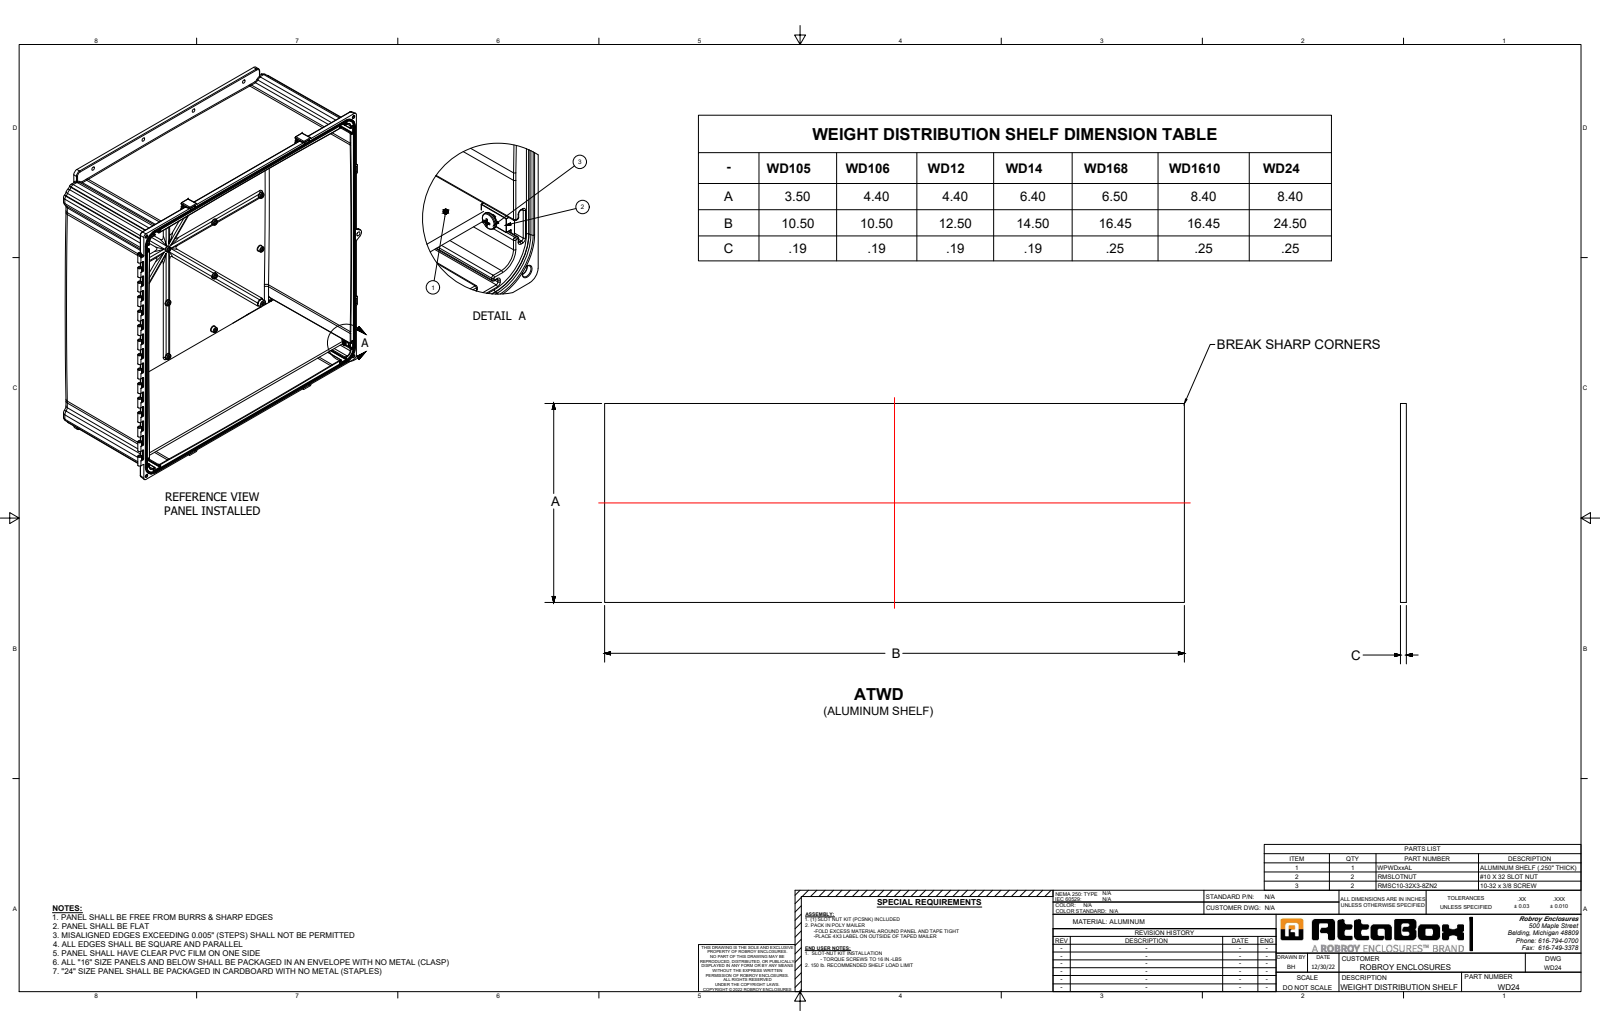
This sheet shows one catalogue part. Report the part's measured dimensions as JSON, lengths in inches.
{"part_name": "WD24_Default", "step_written_by": "SolidWorks 2023 (CONFIG_CONTROL_DESIGN)", "units": "inches", "bodies": {"solids": 1, "faces": 6, "planar": 6, "cylindrical": 0, "other": 0}, "overall_size": [24.5, 8.4, 0.25], "volume_in3": 51.45, "surface_area_in2": 428.1, "face_to_face_distances": [0.25, 8.4, 24.5]}
